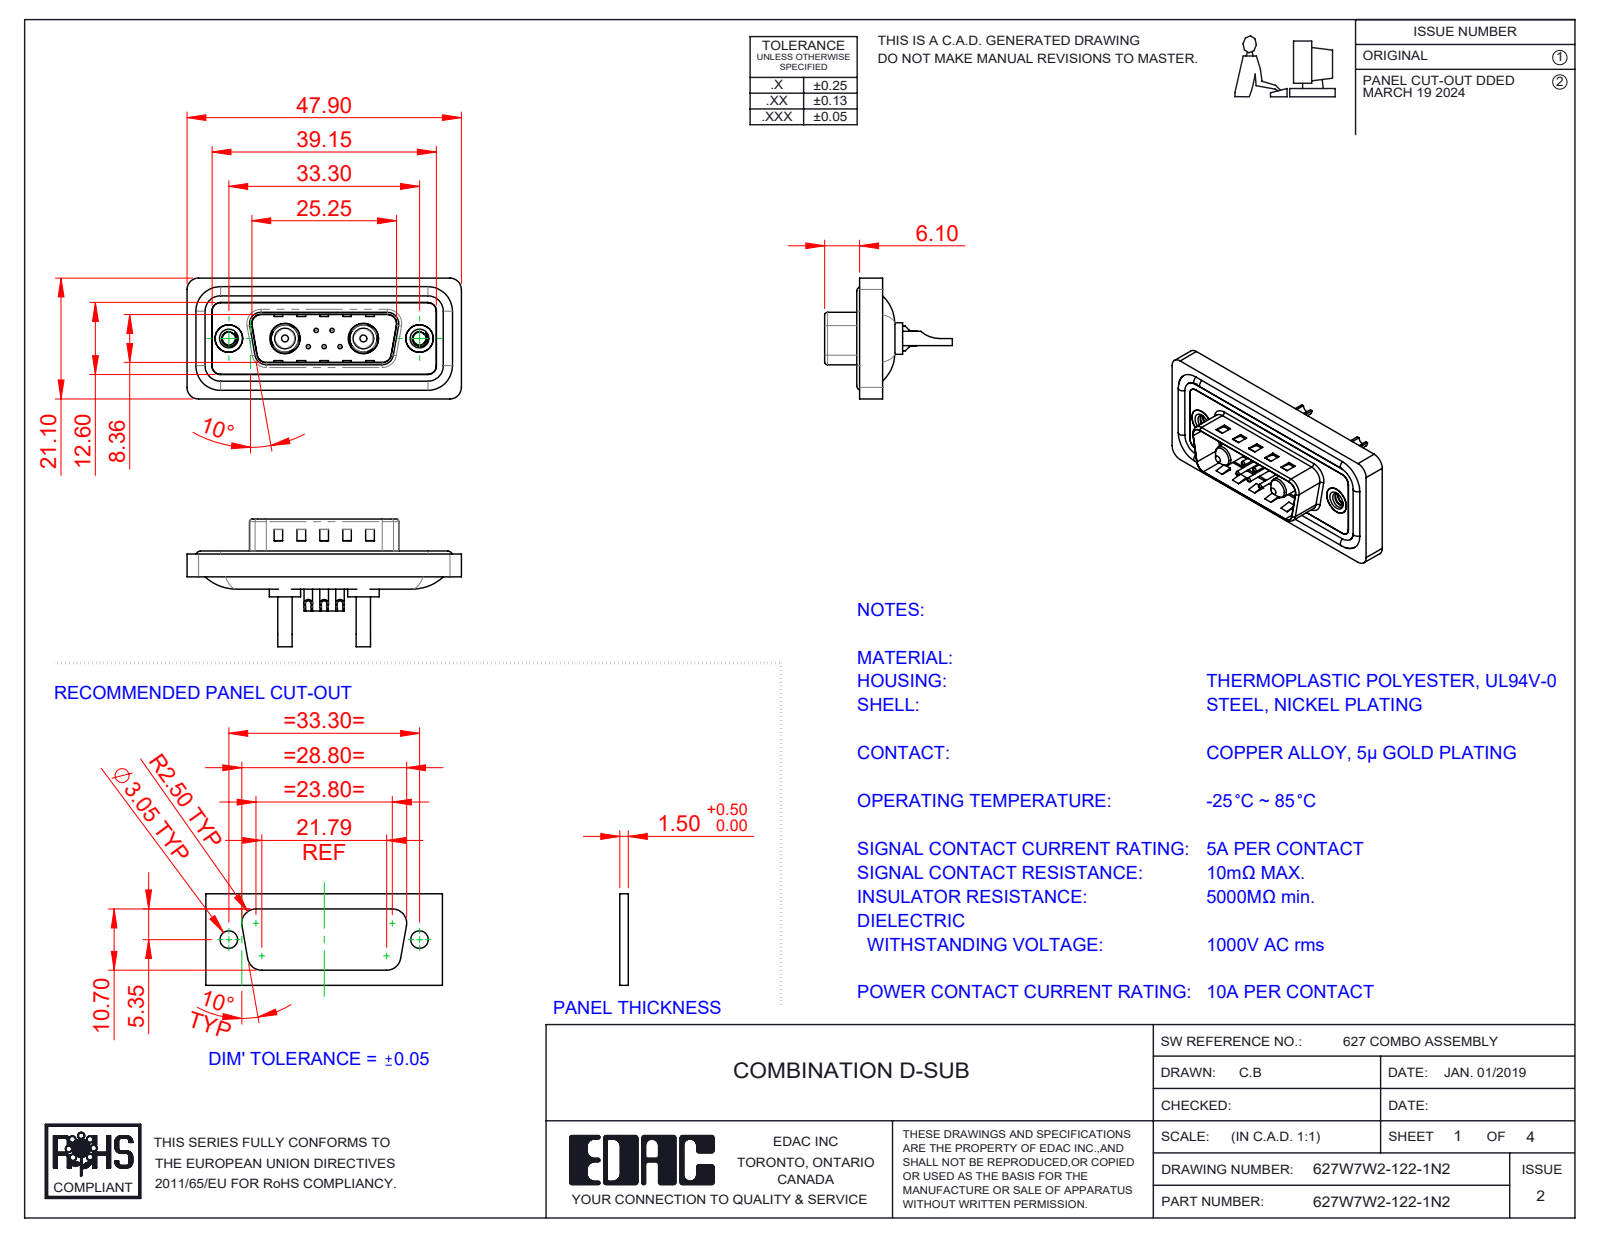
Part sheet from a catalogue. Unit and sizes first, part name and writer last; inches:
Units: inches
Overall size (bounding box): 1.886 × 0.878 × 0.831
Round holes (diameter × count): ⌀0.03 ×5, ⌀0.039 ×5, ⌀0.063 ×5, ⌀0.079 ×5, ⌀0.067 ×2, ⌀0.089 ×2, ⌀0.157 ×2, ⌀0.189 ×2, ⌀0.191 ×2, ⌀0.197 ×2, ⌀0.209 ×2
Round bosses / shafts (diameter × count): ⌀0.059 ×5, ⌀0.063 ×4, ⌀0.217 ×2, ⌀0.205 ×2, ⌀0.193 ×2, ⌀0.187 ×2, ⌀0.148 ×2, ⌀0.142 ×2
Partial cylindrical surfaces — rounded edges, fillets, slot ends (radius × count): R0.059 ×26, R0.079 ×20, R0.02 ×8, R0.063 ×8, R0.039 ×6, R0.01 ×4, R0.024 ×4, R0.026 ×4
Main face-to-face distances: 0.016, 0.043, 0.059, 0.063, 0.02, 0.122, 0.114, 0.157, 0.032, 0.377
Hole centre spacings: 0.124, 0.109, 0.386, 0.925, 0.17, 0.17, 0.198, 0.198
Volume: 0.337 in³ · Surface area: 13.84 in²
Bodies: 16 solids, 720 faces (246 planar, 308 cylindrical, 166 other)
Part name (STEP PRODUCT): 627Combo Threaded Rivet_2; 627Combo Housing_7W2; 627Combo Shell Rear_15 Contacts; 627Combo Contact Row 1_22 (+5 more)
STEP written by: SolidWorks 2023 (CONFIG_CONTROL_DESIGN)
